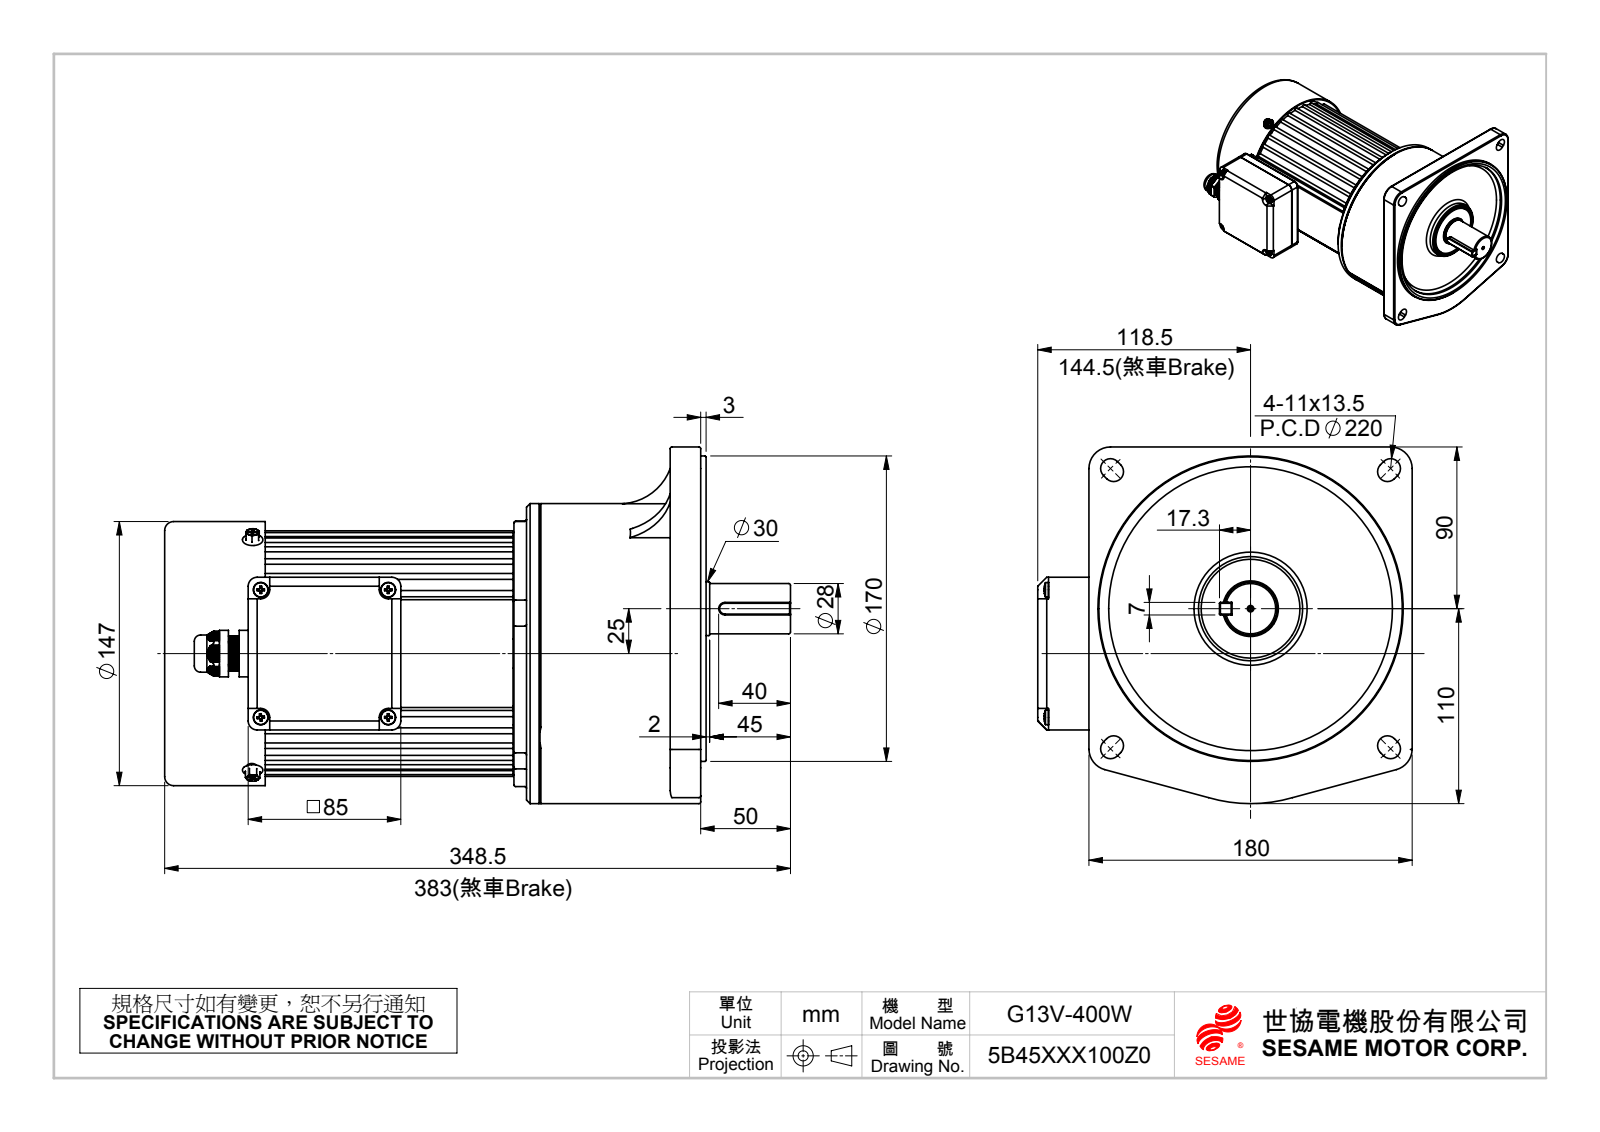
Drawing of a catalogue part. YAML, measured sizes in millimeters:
part_name: "出線盒墊片JTH-UP3(PVC2mm厚); 出線盒上蓋; 出線盒下蓋; G13-750C1-04(含200.400)_G13400C1成品 (+8 more)"
step_written_by: "SolidWorks 2010 (CONFIG_CONTROL_DESIGN)"
units: millimeters
bodies: {solids: 19, faces: 2751, planar: 853, cylindrical: 847, other: 1051}
overall_size: [348.5, 208.5, 198.5]
volume: 5107000
surface_area: 485087
round_holes:
  - {diameter: 5, count: 14}
  - {diameter: 3.3, count: 9}
  - {diameter: 8, count: 9}
  - {diameter: 5.1, count: 5}
  - {diameter: 6, count: 5}
  - {diameter: 2, count: 1}
  - {diameter: 10.8, count: 1}
  - {diameter: 16.5, count: 1}
  - {diameter: 30, count: 1}
  - {diameter: 31, count: 1}
  - {diameter: 53, count: 1}
  - {diameter: 55, count: 1}
round_bosses_or_shafts:
  - {diameter: 8.3, count: 4}
  - {diameter: 4, count: 4}
  - {diameter: 5, count: 2}
  - {diameter: 170, count: 1}
  - {diameter: 167, count: 1}
  - {diameter: 158, count: 1}
  - {diameter: 148, count: 1}
  - {diameter: 147, count: 1}
partial_cylinders:
  - {radius: 1, count: 36}
  - {radius: 1.85, count: 31}
  - {radius: 0.5, count: 24}
  - {radius: 3, count: 16}
  - {radius: 5, count: 8}
  - {radius: 5.5, count: 8}
  - {radius: 2.75, count: 6}
  - {radius: 8, count: 5}
face_to_face_distances: [5, 84.5, 15, 20, 12, 160, 155, 227.5, 9.5, 164.5]
hole_center_spacings: [45, 63.67, 71, 144.57, 76.01, 89.35, 11, 11.5]
